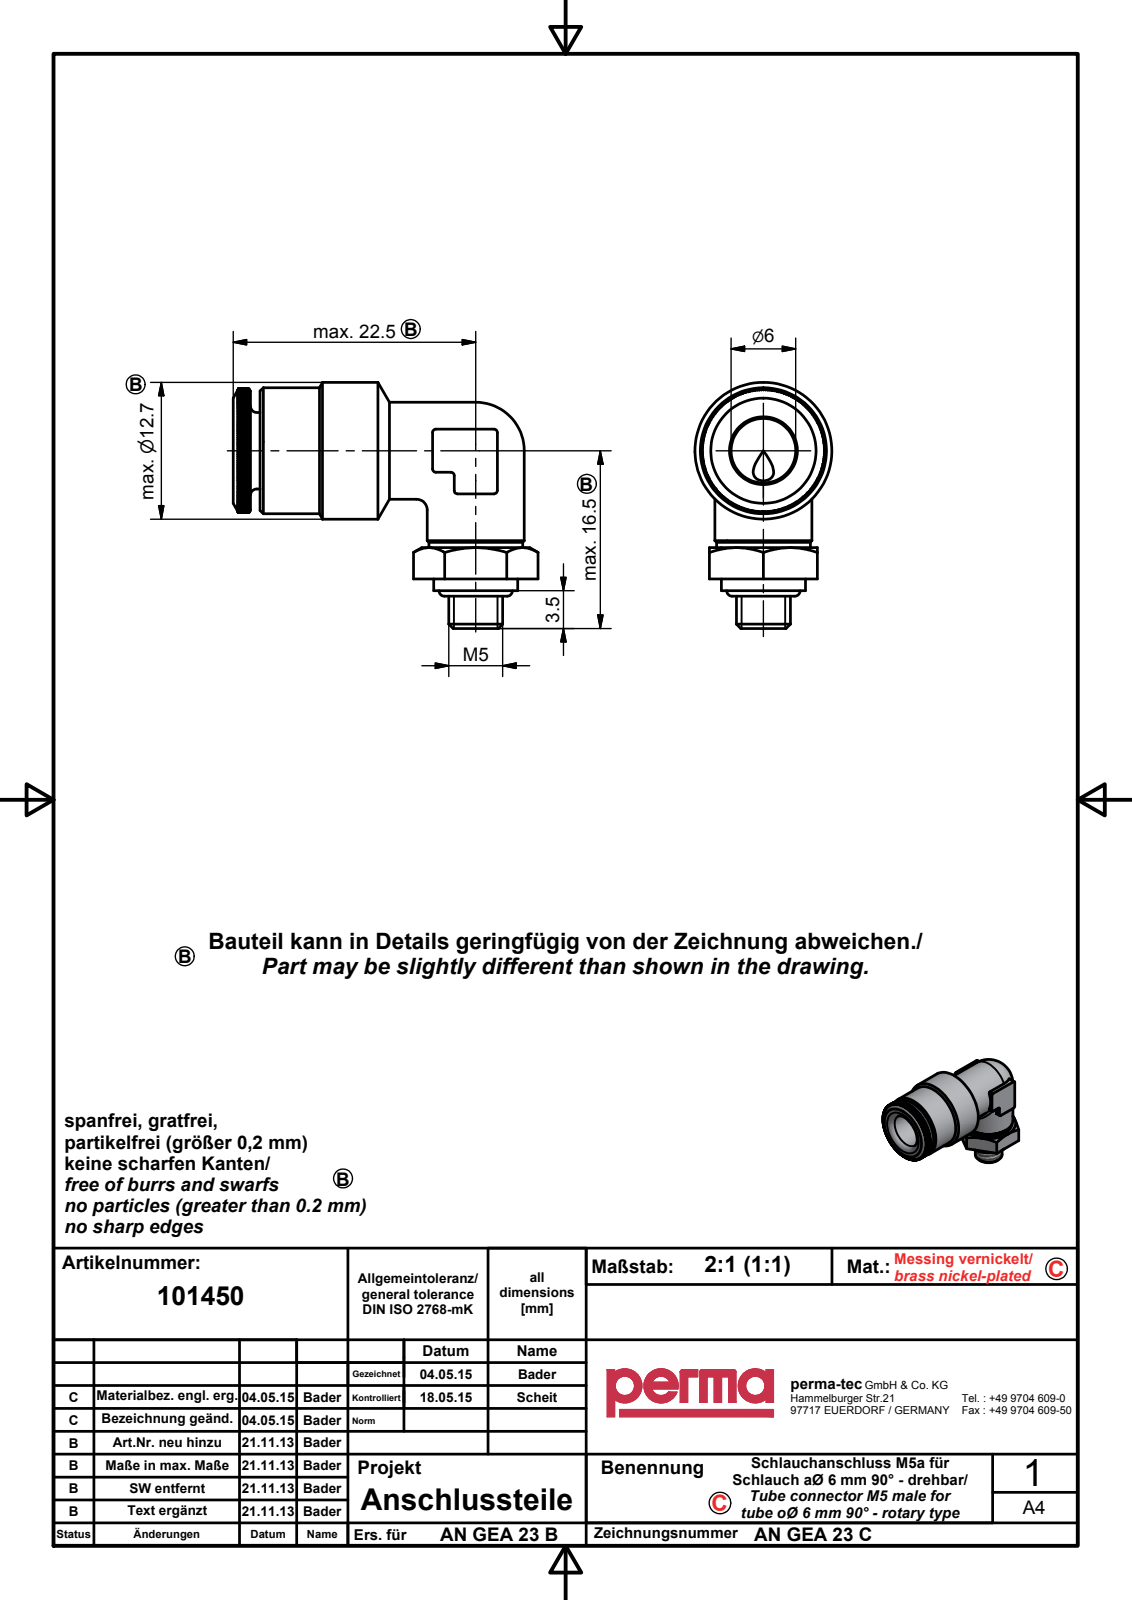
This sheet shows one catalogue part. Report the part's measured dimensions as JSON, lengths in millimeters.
{"part_name": "angea23a", "step_written_by": "Autodesk Inventor 10 (AUTOMOTIVE_DESIGN)", "units": "millimeters", "bodies": {"solids": 1, "faces": 671, "planar": 428, "cylindrical": 222, "other": 21}, "overall_size": [28.27, 22.85, 12.7], "volume_mm3": 2307, "surface_area_mm2": 2088, "round_holes": [[1.9, 1], [6, 1]], "round_bosses_or_shafts": [[9, 2], [12.7, 1], [11.7, 1], [8.7, 1], [7.8, 1], [7.1, 1], [5, 1]], "partial_cylinders_radius": [[0.3, 6], [5.75, 1]], "face_to_face_distances": [0.9, 9.7, 9.85, 9.99, 1.6, 2.5, 2.9, 4, 10, 18.5]}
